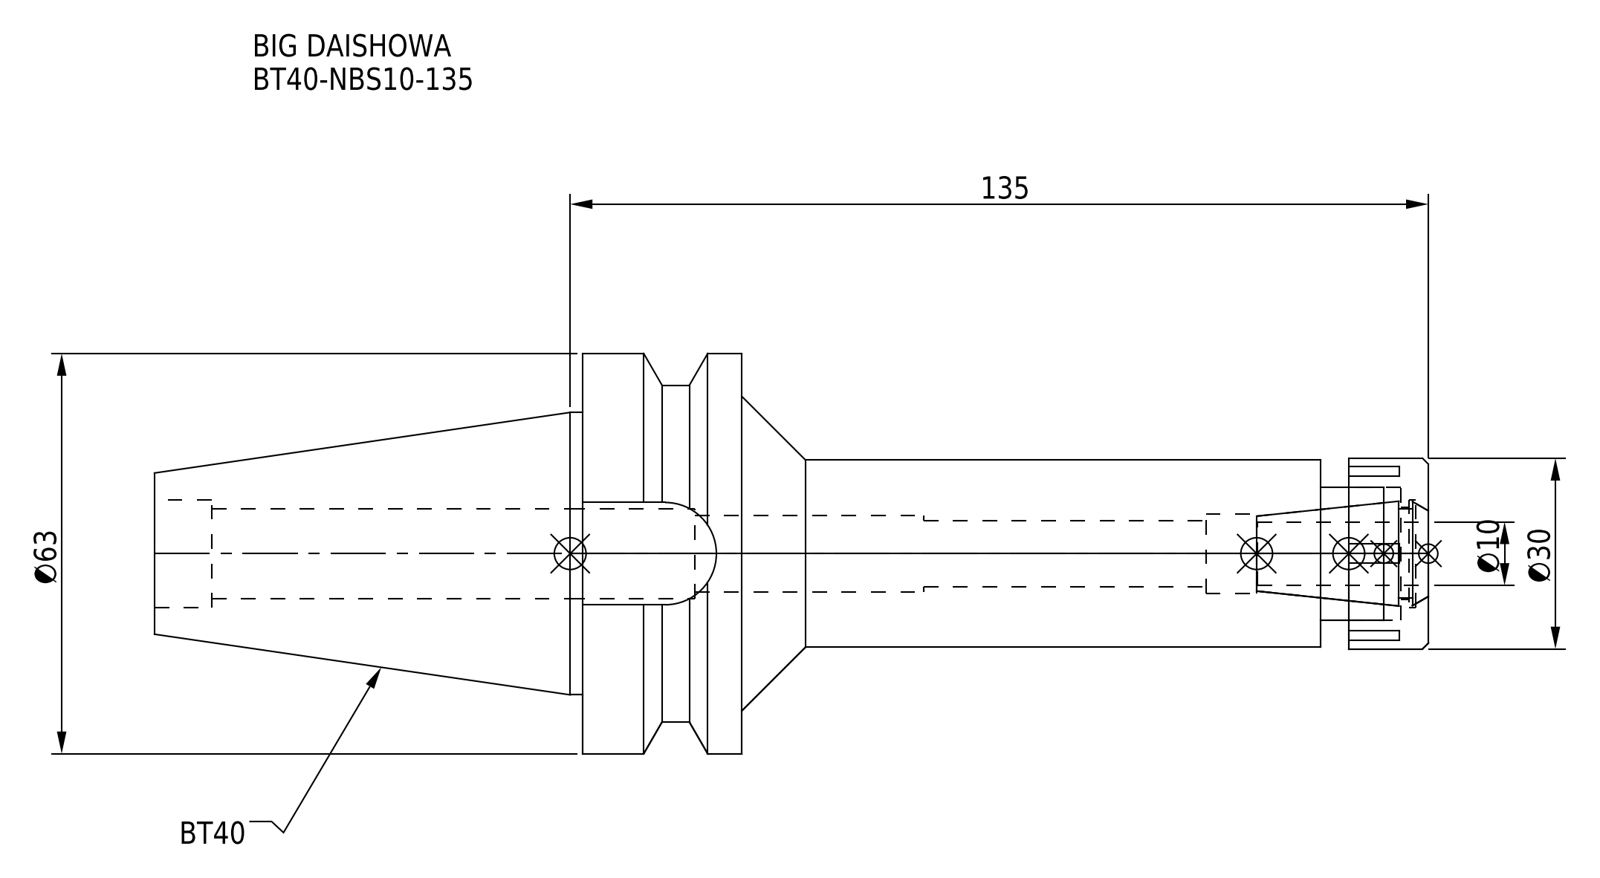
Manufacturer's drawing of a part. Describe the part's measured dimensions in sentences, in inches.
The part is named "DXF_TEMP_ASSY_ASM_4_ASM.stp; BT40NB10135-100_ASM.stp; BT40-NBS10-135.stp; NBN10_1.stp (+3 more)". Its 3-D file was written by "SolidWorks 2019 (CONFIG_CONTROL_DESIGN)". It is 2 solids with 93 faces: 45 planar, 34 cylindrical and 14 other. Overall it measures 7.89 by 2.48 by 2.48 inches. Its volume is 11.26 cubic inches and its surface area 59.38 square inches. Round holes: 1 of diameter 0.409, 1 of diameter 0.472, 1 of diameter 0.492, 1 of diameter 0.559, 1 of diameter 0.571, 1 of diameter 0.669, 1 of diameter 0.827. Round bosses or shafts: 1 of diameter 2.48, 1 of diameter 2.087, 1 of diameter 1.75, 1 of diameter 1.181, 1 of diameter 1.161. Partial cylindrical surfaces (rounded edges, fillets, slot ends): 1 of radius 0.317. The main face-to-face distances are 0.984, 4.252, 5.236, 0.177, 0.492, 0.669, 3.583, 4.567, 3.76, 4.744.
